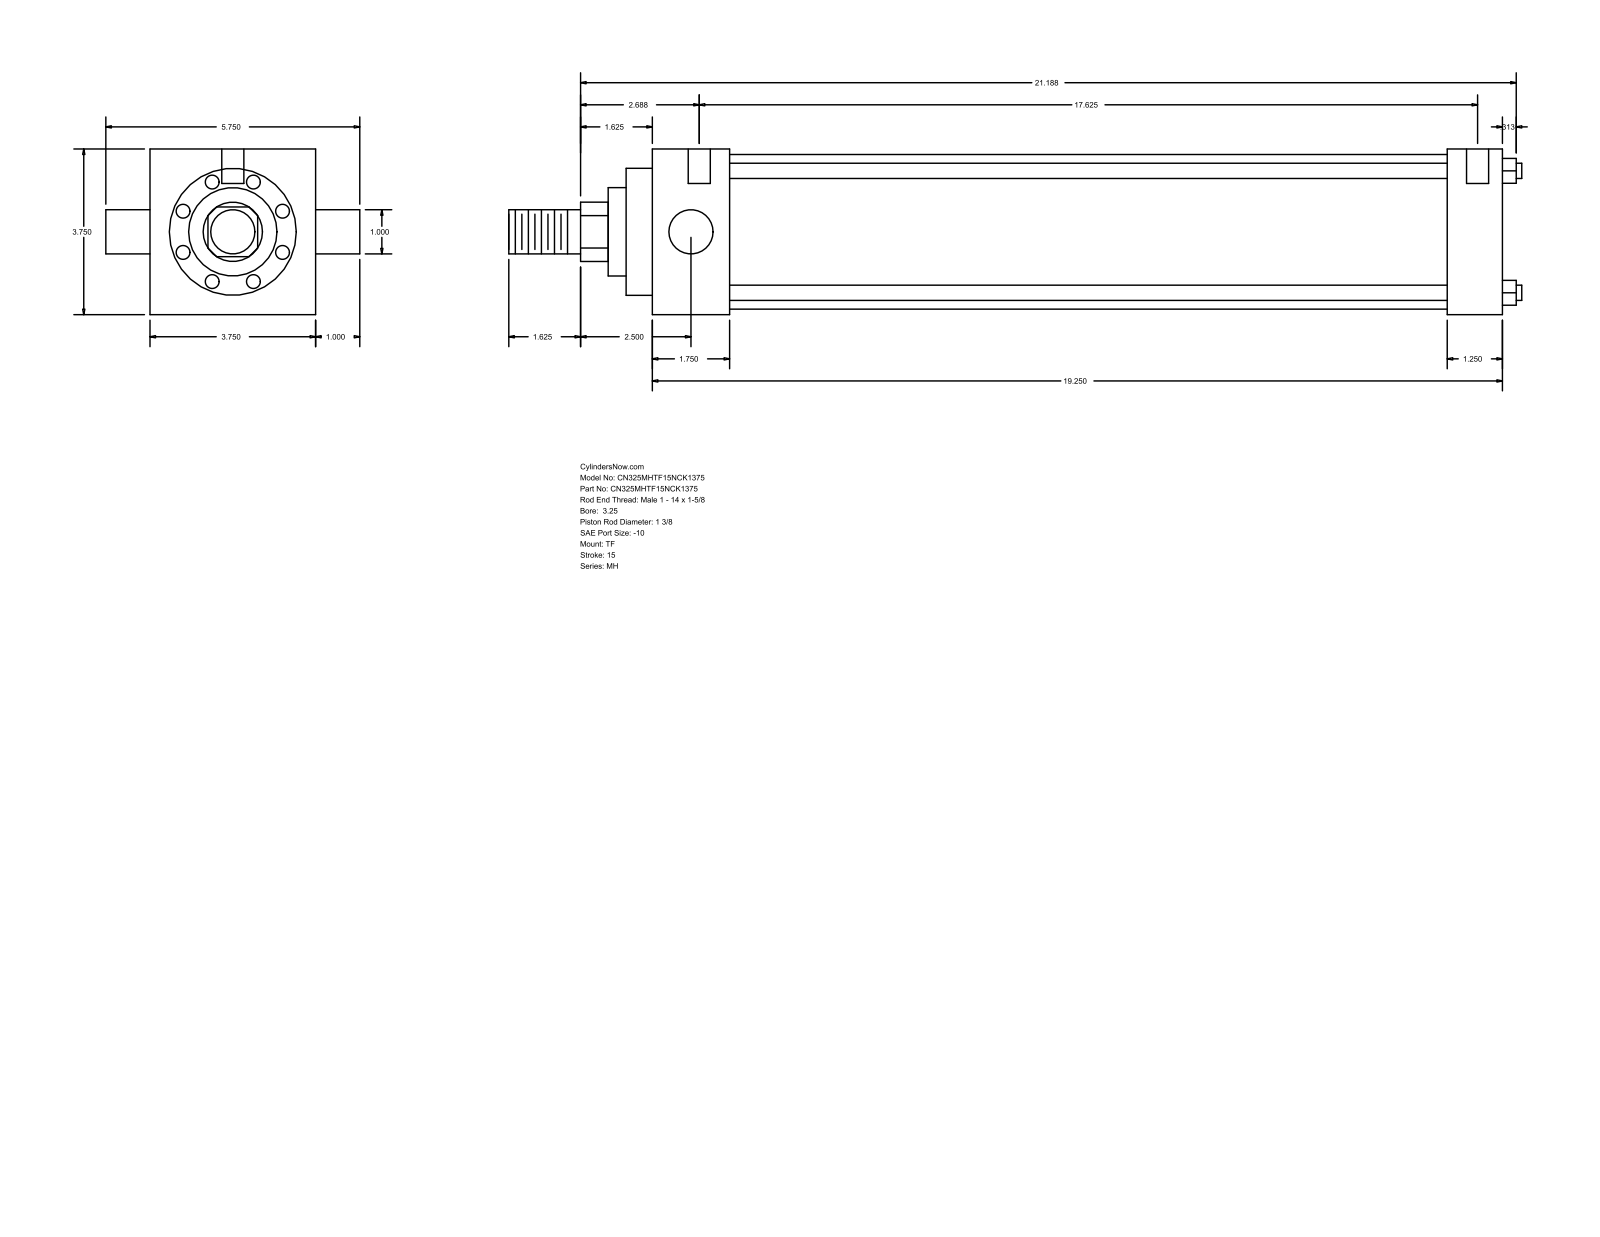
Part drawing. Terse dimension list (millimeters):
name: MH_TF__0325_1.375
written by: GSSL Pune (CONFIG_CONTROL_DESIGN)
unit: mm
bodies: 0 solids, 86 faces (61 planar, 25 cylindrical, 0 other)
size: 582.61 × 146.05 × 95.25
holes: 3× ⌀5.56, 2× ⌀12.7
bosses: 4× ⌀8.76, 2× ⌀25.4, 1× ⌀88.9, 1× ⌀73.03, 1× ⌀50.8, 1× ⌀34.92
rounds: 1× R17.06
face distances: 95.24, 488.96, 44.45, 457.21, 412.76, 444.51, 31.75, 15.08, 59.53, 472.29
hole spacings: 1.59, 4.76, 447.68, 449.27, 452.44, 454.03
